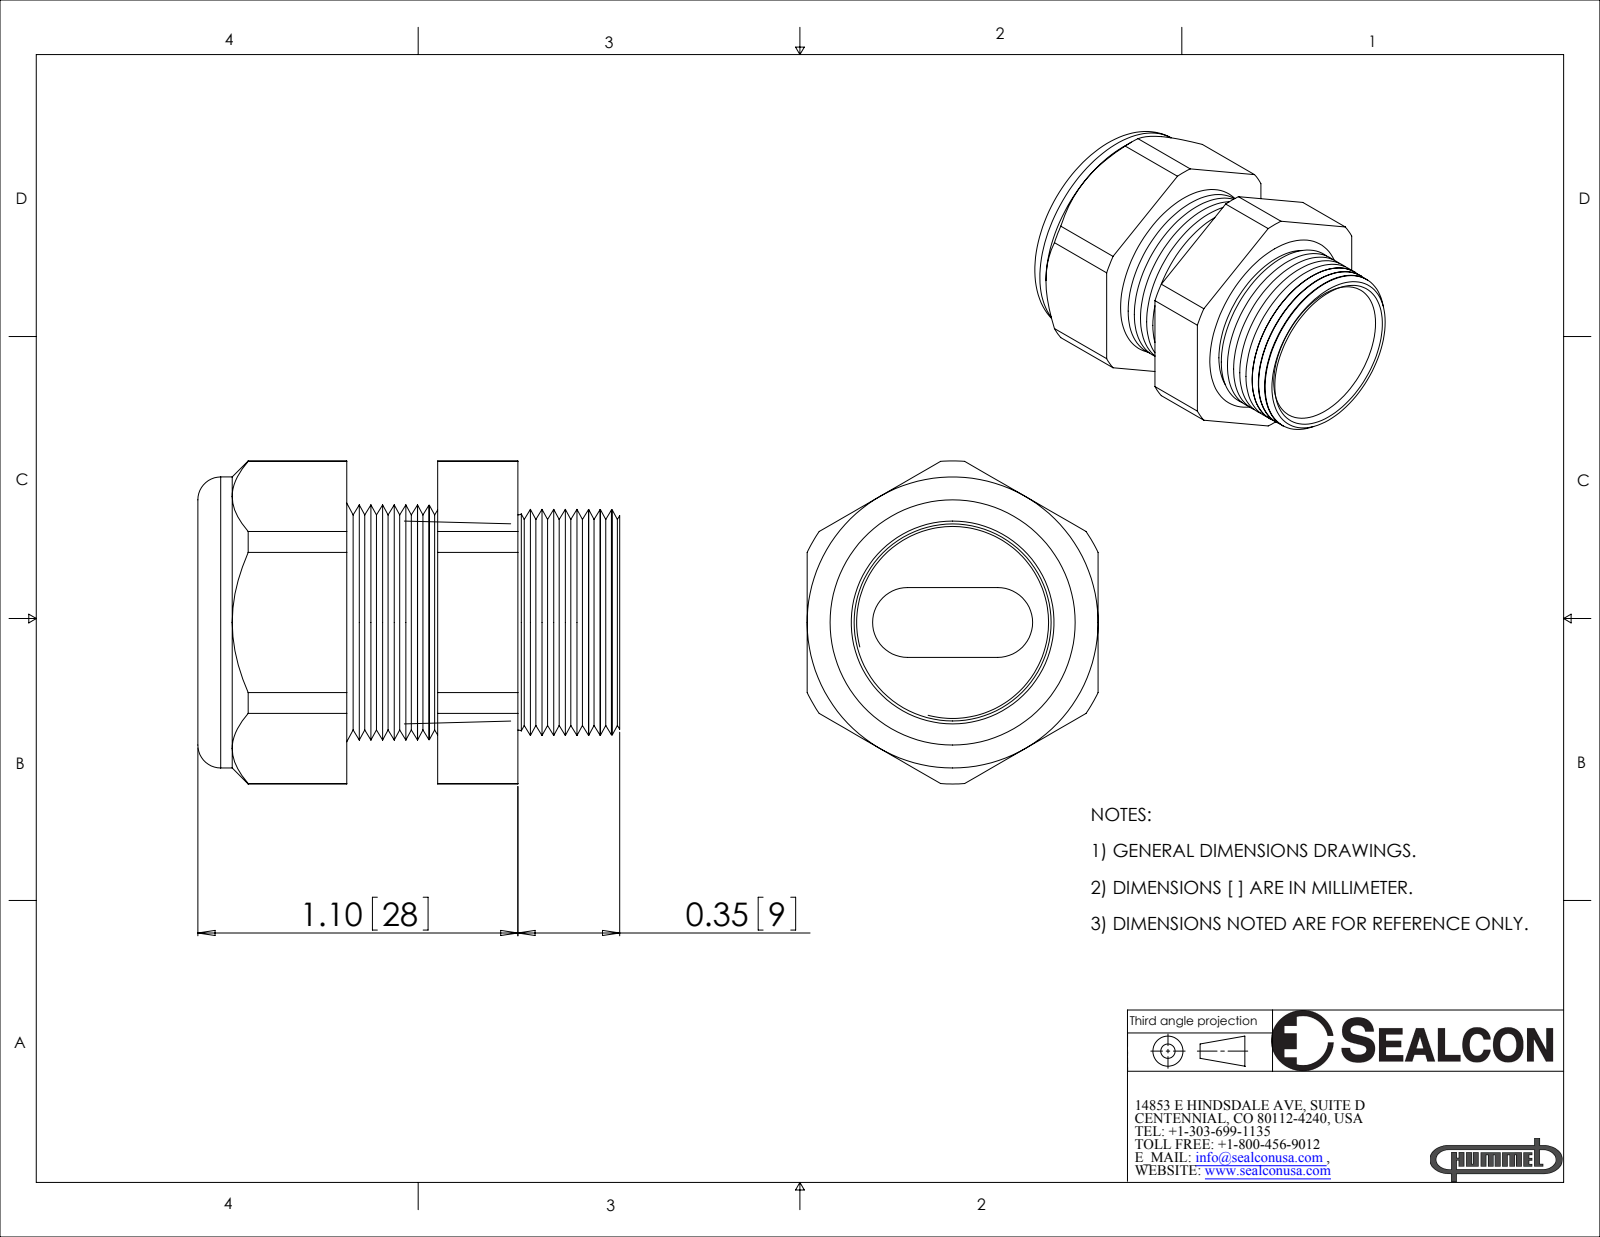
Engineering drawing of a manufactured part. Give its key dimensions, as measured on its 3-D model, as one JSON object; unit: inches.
{"part_name": "CD16NS-02", "step_written_by": "SolidWorks 2007 (CONFIG_CONTROL_DESIGN)", "units": "inches", "bodies": {"solids": 2, "faces": 133, "planar": 21, "cylindrical": 20, "other": 92}, "overall_size": [1.45, 1.11, 1], "volume_in3": 0.5, "surface_area_in2": 12.41, "round_holes": [[0.697, 1]], "round_bosses_or_shafts": [[1, 1], [0.677, 1]], "partial_cylinders_radius": [[0.12, 2], [0.555, 1]], "face_to_face_distances": [1, 0.824, 0.512, 0.313, 1.1, 0.588, 0.276, 0.394, 0.118, 0.431]}
